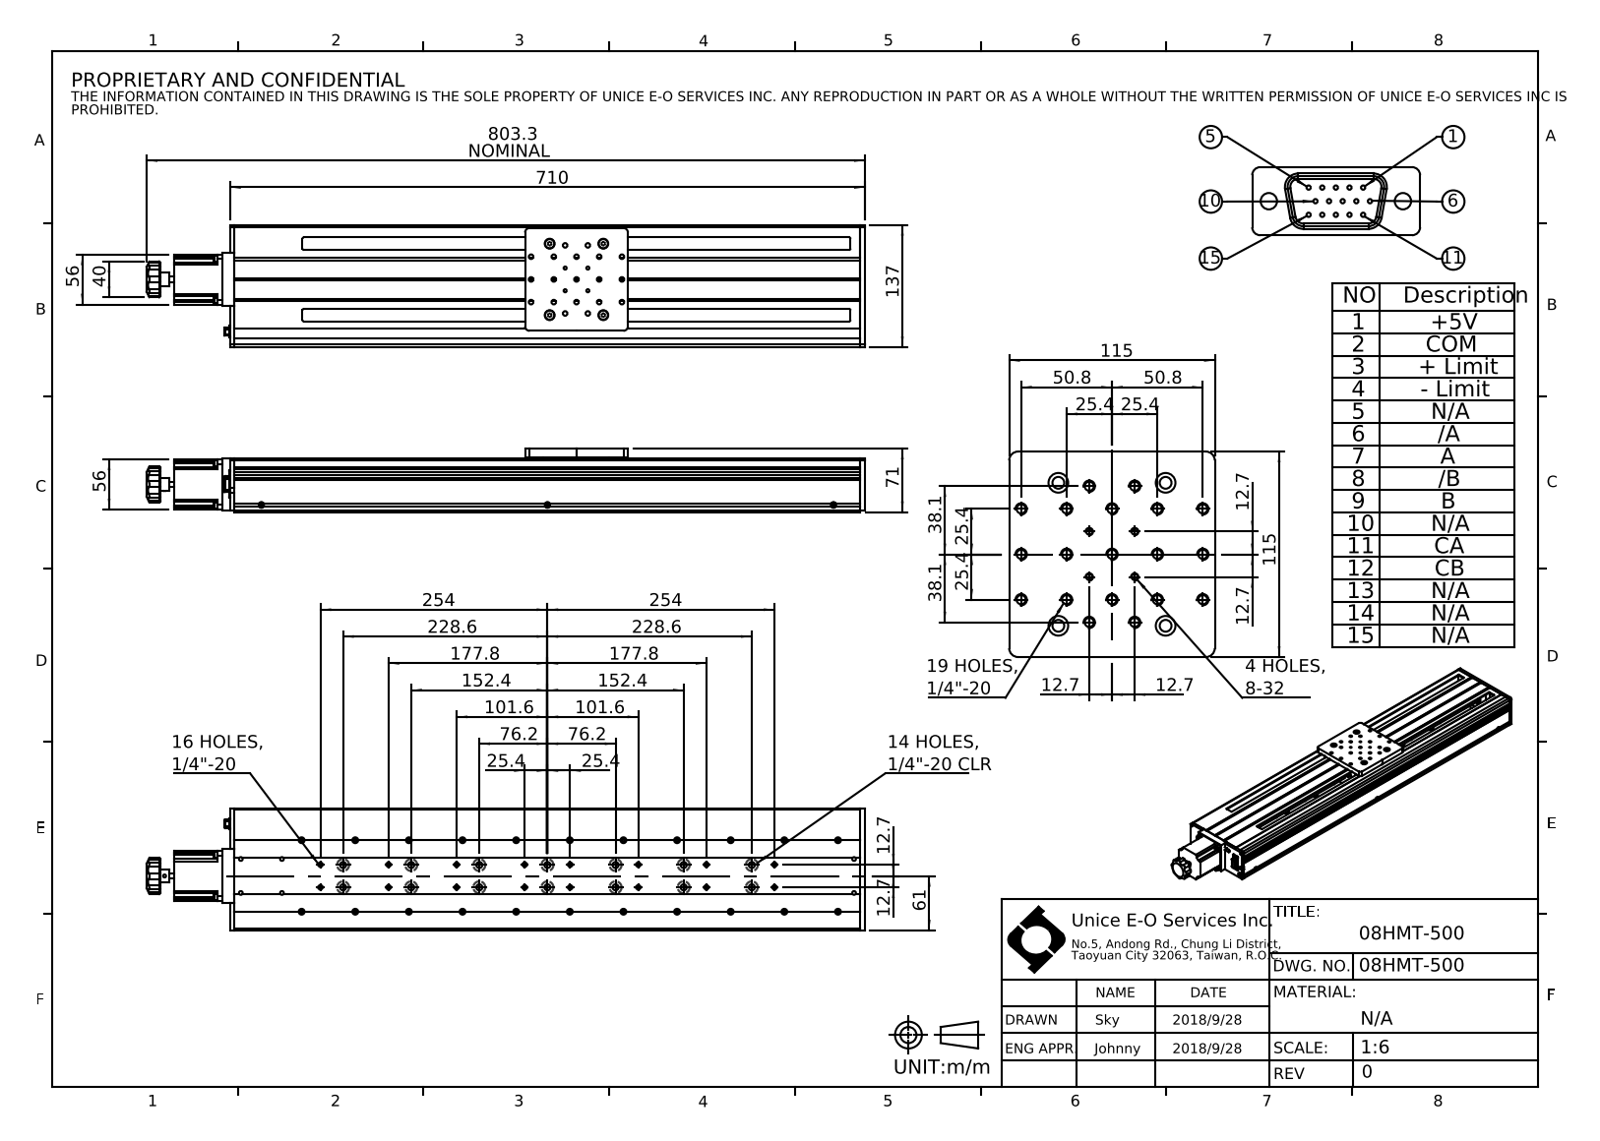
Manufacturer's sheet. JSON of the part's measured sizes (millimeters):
{"part_name": "08HMT-500", "step_written_by": "SolidWorks 2016 (AUTOMOTIVE_DESIGN)", "units": "millimeters", "bodies": {"solids": 0, "faces": 803, "planar": 354, "cylindrical": 341, "other": 108}, "overall_size": [803.3, 137, 71], "round_holes": [[5.11, 35], [6.5, 22], [6.76, 14], [13.49, 12], [0.8, 8], [4.2, 6], [3.45, 4], [11, 4], [2, 2], [2.26, 2], [3.3, 2], [18, 1]], "round_bosses_or_shafts": [[6.5, 4], [5.8, 3], [7.7, 2], [7, 2], [15, 1], [14, 1], [6.35, 1]], "partial_cylinders_radius": [[1.5, 8], [4, 8], [5, 8], [7.41, 8], [0.5, 4], [2, 4], [4.5, 4], [3, 3]], "face_to_face_distances": [2, 60.5, 135, 133, 10.5, 1.5, 59, 137, 1.7, 9], "hole_center_spacings": [40.16, 25.4, 17.96, 56.8, 35.92, 64.76, 50.8, 53.88]}
